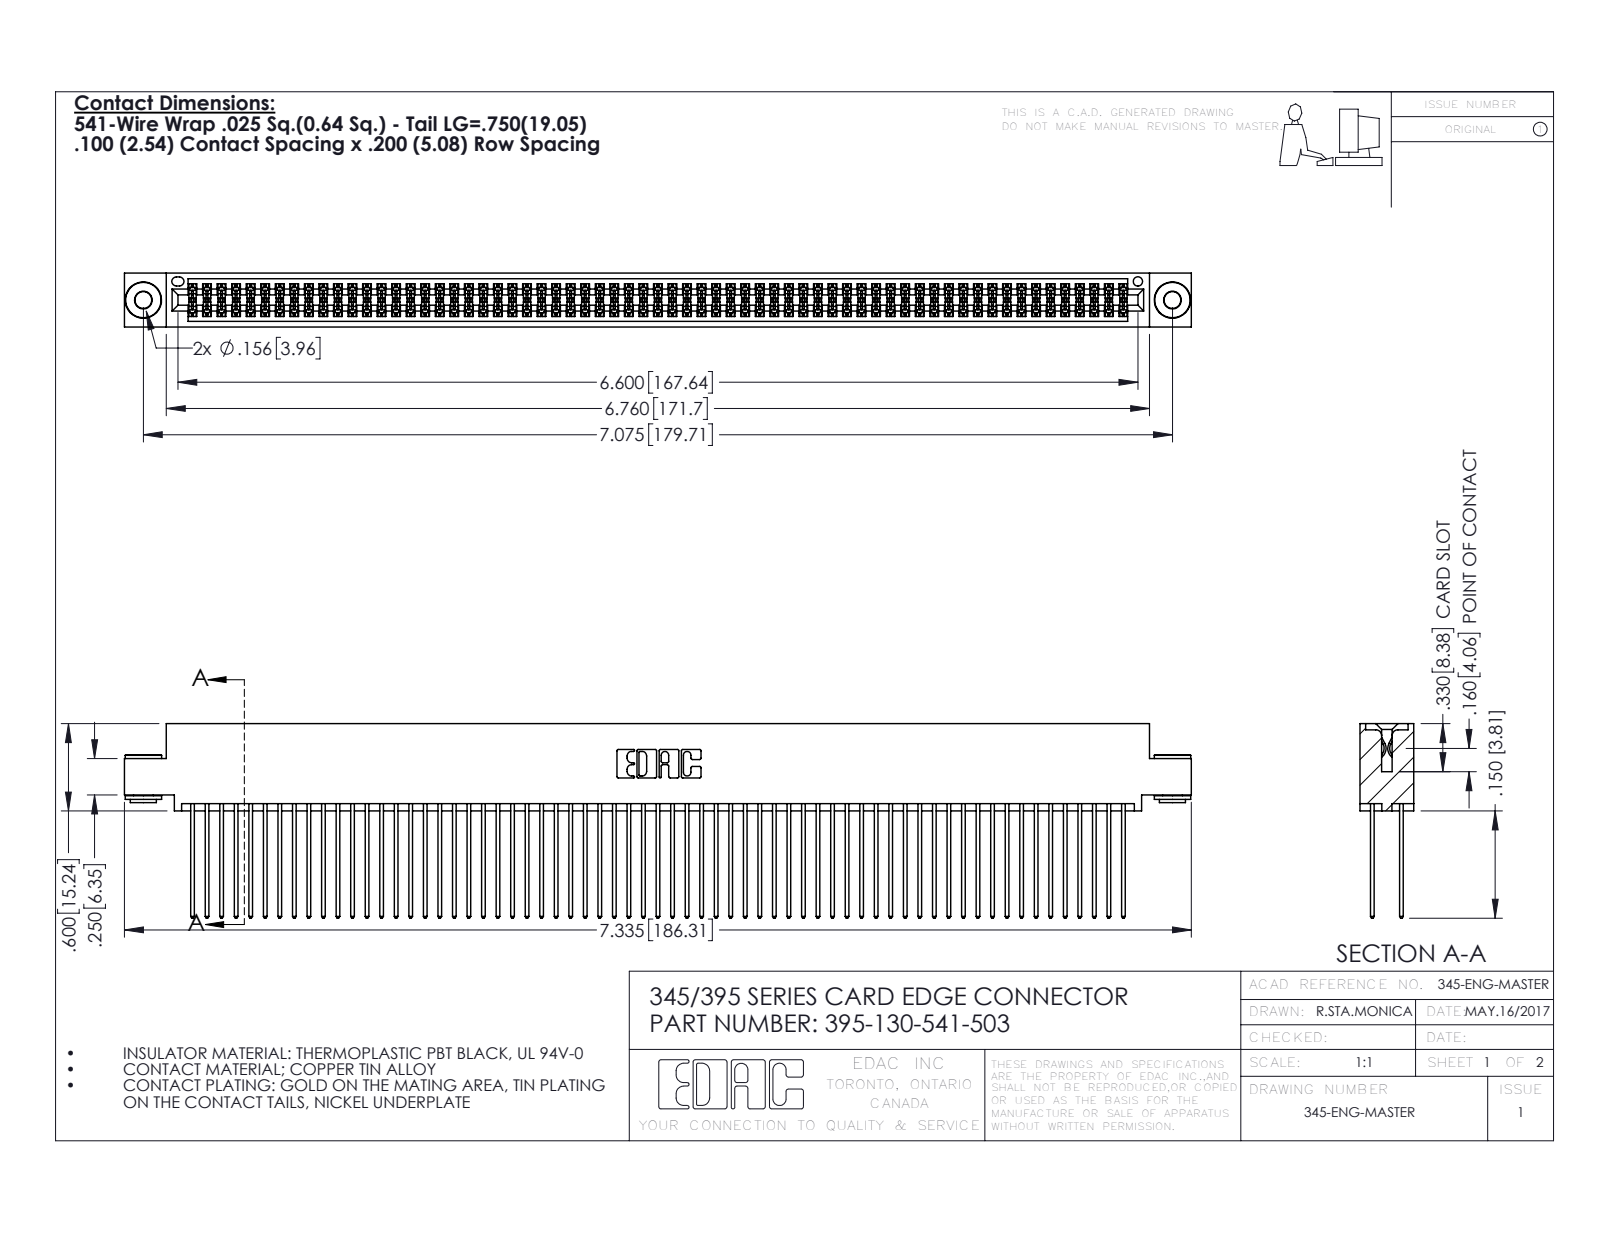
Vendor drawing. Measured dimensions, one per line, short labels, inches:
name: 345-292-001_345-293-141; 345 Part_0.110 Offset - 0.156 Dia-TH; 345-250-002_345-250-002-102; 395-130-541-503
written by: SolidWorks 2016 (CONFIG_CONTROL_DESIGN)
unit: in
bodies: 133 solids, 6668 faces (4384 planar, 2276 cylindrical, 8 other)
size: 7.335 × 1.337 × 0.37
volume: 1.16 in³; area: 50.13 in²
holes: 2× ⌀0.116, 2× ⌀0.156, 1× ⌀0.064
bosses: 2× ⌀0.25, 2× ⌀0.18, 2× ⌀0.136
rounds: 195× R0.006, 130× R0.01, 22× R0.01, 6× R0.007, 6× R0.031, 3× R0.026, 2× R0.014, 2× R0.019
face distances: 0.072, 0.298, 0.2, 0.025, 0.098, 0.272, 0.225, 0.37, 0.175, 0.149
hole spacings: 0.27, 6.839, 7.075
